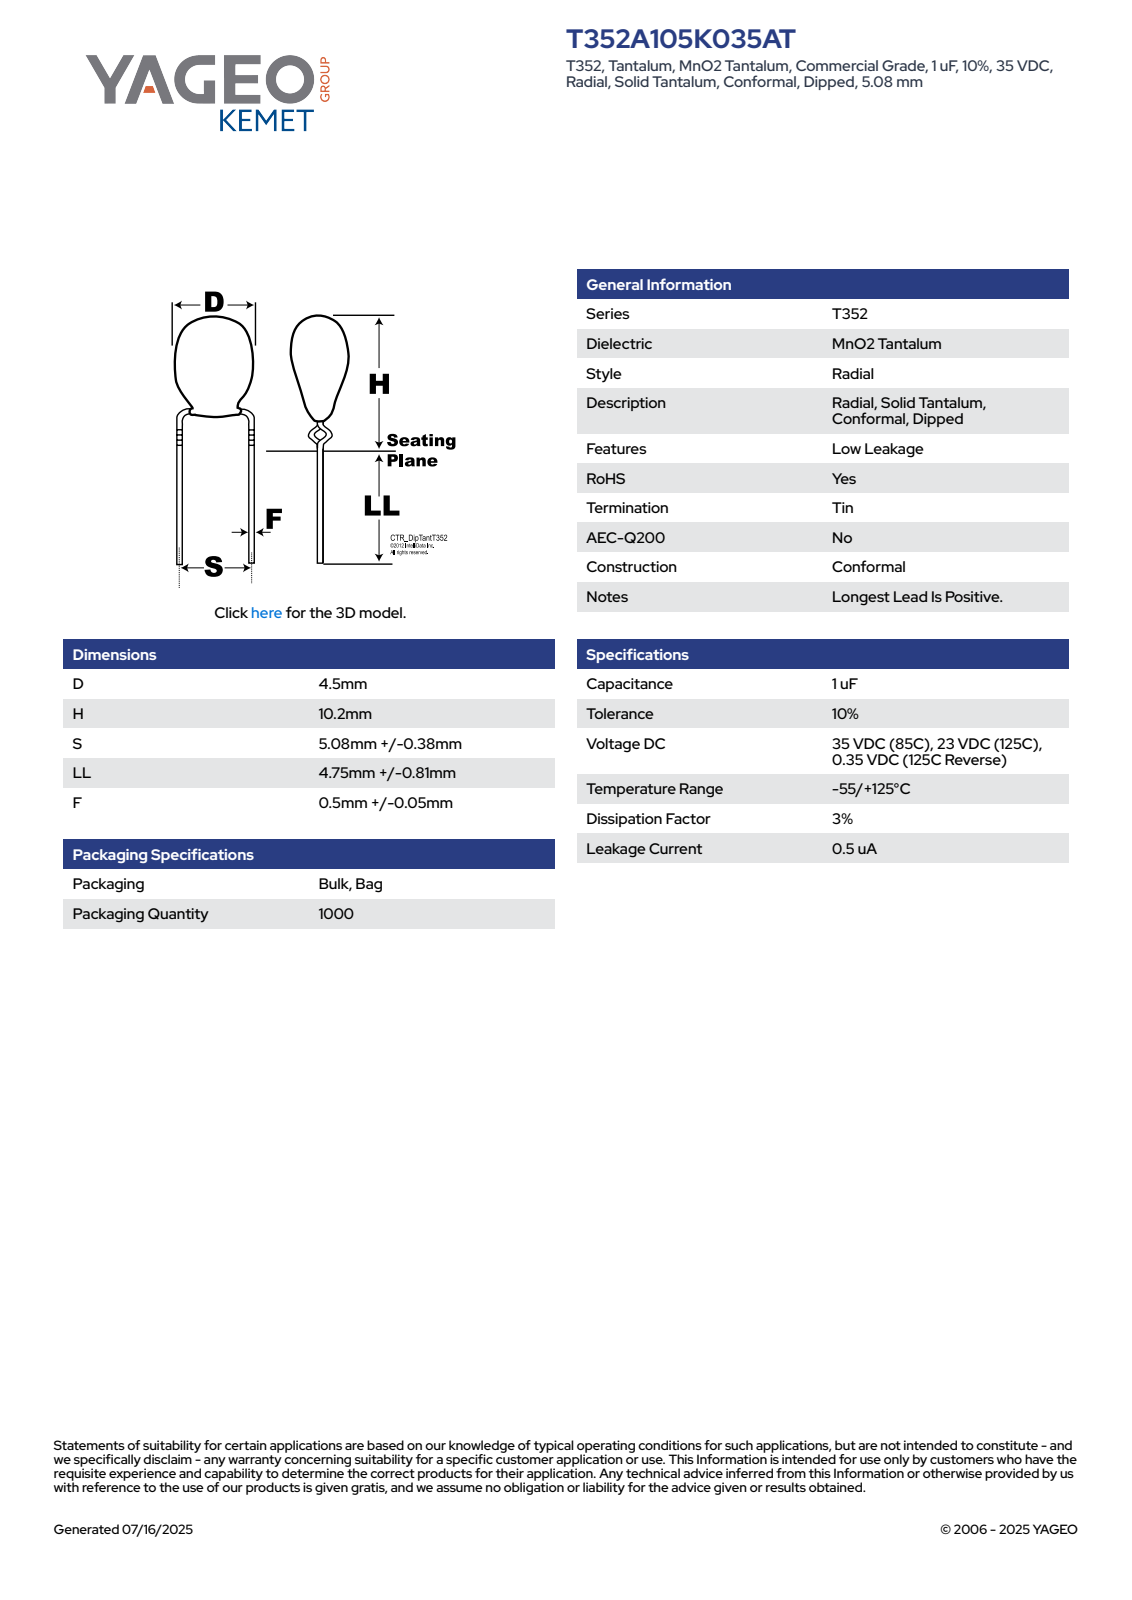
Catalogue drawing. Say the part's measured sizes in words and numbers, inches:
The part is named "CTR_T352_D4.5H10.2S5.08LL5.56F0.55". Its 3-D file was written by "SolidWorks 2014 (AUTOMOTIVE_DESIGN)". It is 1 solid with 93 faces: 26 planar, 14 cylindrical and 53 other. Overall it measures 0.62 by 0.222 by 0.177 inches. Its volume is 0.007 cubic inches and its surface area 0.251 square inches. Round bosses or shafts: 3 of diameter 0.022, 1 of diameter 0.177. Partial cylindrical surfaces (rounded edges, fillets, slot ends): 1 of radius 0.088. The main face-to-face distances are 0.315, 0.156, 0.159, 0.131, 0.024, 0.183, 0.019, 0.136, 0.179, 0.146.
